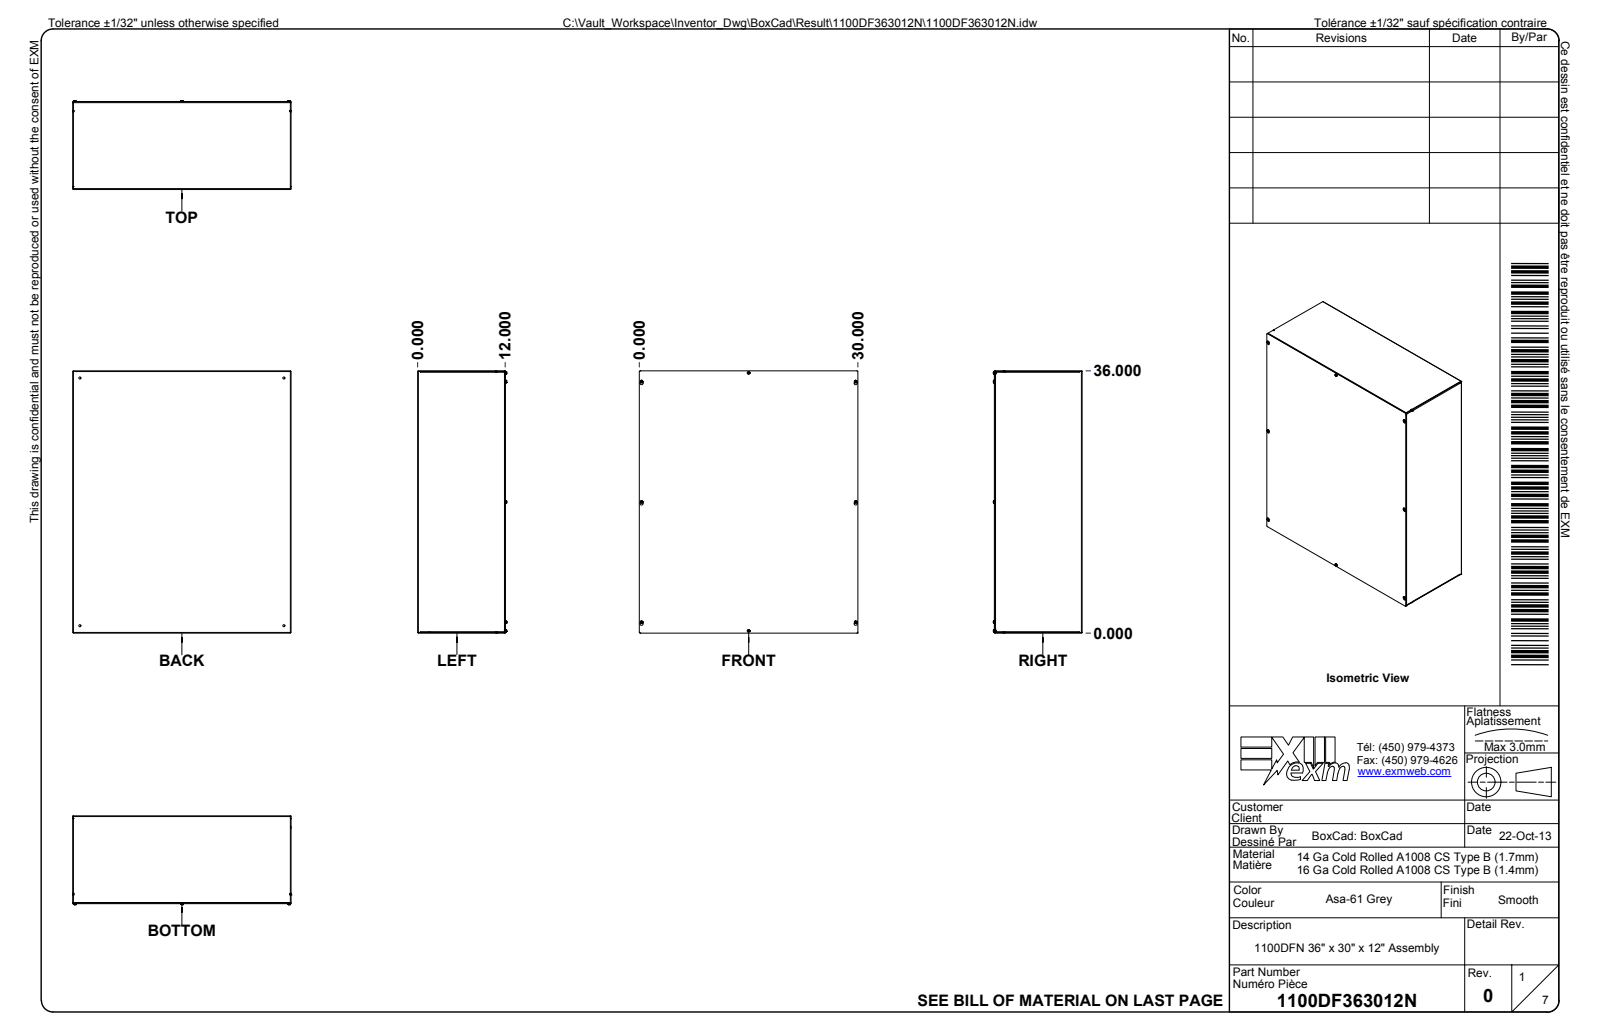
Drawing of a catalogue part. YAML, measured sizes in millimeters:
part_name: "1100DF363012N; 1100DF363012NB; 1100DF363012NB-P; 1100DF363012NC (+5 more)"
step_written_by: "Autodesk Inventor 2024 (AUTOMOTIVE_DESIGN)"
units: millimeters
bodies: {solids: 12, faces: 4287, planar: 2490, cylindrical: 625, other: 1172}
overall_size: [914.4, 762, 309.4]
volume: 3974000
surface_area: 4928000
round_holes:
  - {diameter: 4.2, count: 8}
  - {diameter: 7.4, count: 6}
  - {diameter: 10.3, count: 6}
  - {diameter: 0.8, count: 2}
  - {diameter: 4.5, count: 2}
  - {diameter: 1.1, count: 1}
  - {diameter: 7.9, count: 1}
  - {diameter: 27, count: 1}
round_bosses_or_shafts:
  - {diameter: 9.5, count: 8}
  - {diameter: 0.8, count: 2}
  - {diameter: 31.8, count: 1}
  - {diameter: 29, count: 1}
  - {diameter: 6.4, count: 1}
  - {diameter: 1.3, count: 1}
partial_cylinders:
  - {radius: 0.1, count: 56}
  - {radius: 1.5, count: 24}
  - {radius: 2.8, count: 24}
  - {radius: 0.8, count: 14}
  - {radius: 2.5, count: 14}
  - {radius: 3, count: 6}
  - {radius: 1.6, count: 4}
  - {radius: 2.4, count: 4}
face_to_face_distances: [1.7, 303.1, 1.3, 304.8, 306.1, 304.4, 760.3, 912.7, 762, 758.5]
hole_center_spacings: [419.1, 856.3, 5.6, 746.8, 746.8, 21.8, 356, 374.6]
